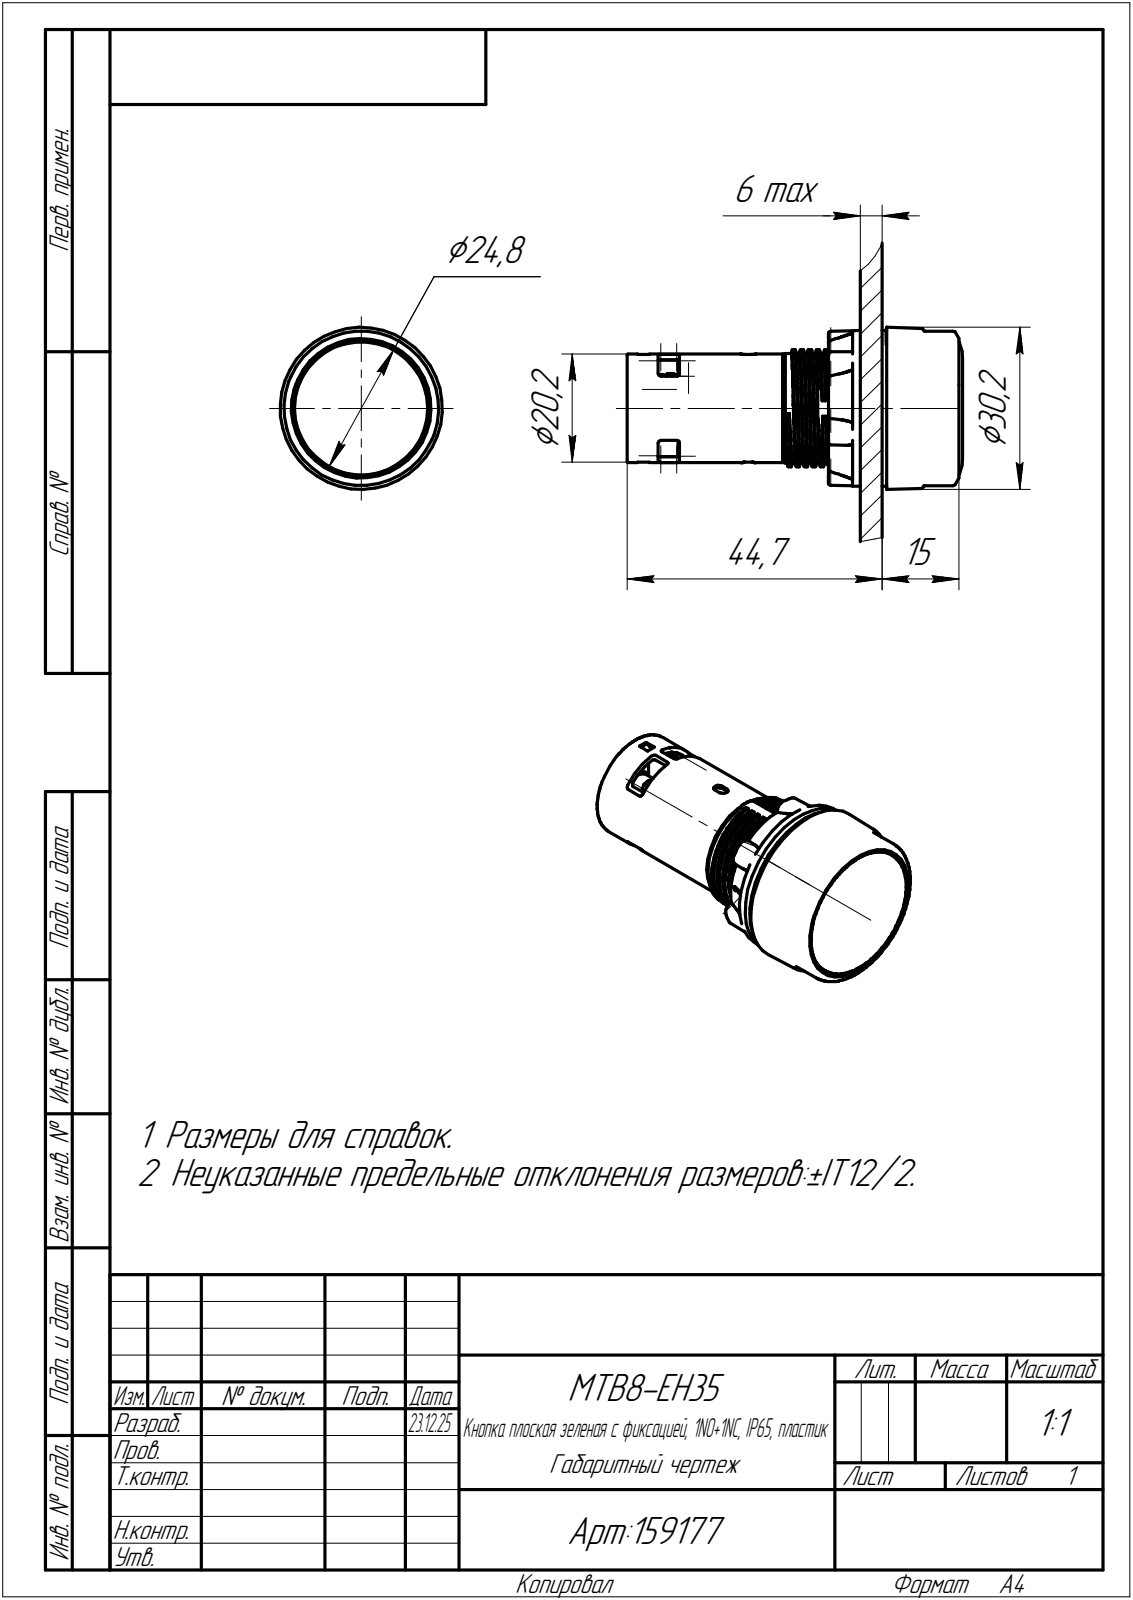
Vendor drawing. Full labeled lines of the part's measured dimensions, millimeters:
Part name (STEP PRODUCT): MTB8-EH35
STEP written by: C3D Toolkit (CONFIG_CONTROL_DESIGN)
Units: millimetres
Bodies: 17 solids, 2516 faces (976 planar, 755 cylindrical, 785 other)
Overall size (bounding box): 59.7 × 30.2 × 30.2
Volume: 22 520 mm³ · Surface area: 12 883 mm²
Round holes (diameter × count): ⌀2.5 ×8, ⌀2 ×4, ⌀6.2 ×4, ⌀18.1 ×1, ⌀22.4 ×1, ⌀23 ×1, ⌀23.3 ×1, ⌀25.1 ×1, ⌀28.2 ×1, ⌀29.2 ×1
Round bosses / shafts (diameter × count): ⌀5.6 ×4, ⌀3.9 ×4, ⌀3 ×4, ⌀2.4 ×4, ⌀29 ×1, ⌀28.8 ×1, ⌀24.8 ×1, ⌀22 ×1
Partial cylindrical surfaces — rounded edges, fillets, slot ends (radius × count): R0.1 ×180, R0.2 ×40, R0.3 ×36, R0.5 ×28, R0.15 ×27, R0.25 ×8, R1.3 ×8, R0.4 ×7
Main face-to-face distances: 1.2, 13.4, 1, 6, 7.2, 14.6, 12.2, 10.6, 7.6, 2.3
Hole centre spacings: 1.56, 5.17, 5.24, 5.25, 5.66, 5.94, 6.73, 7.7
